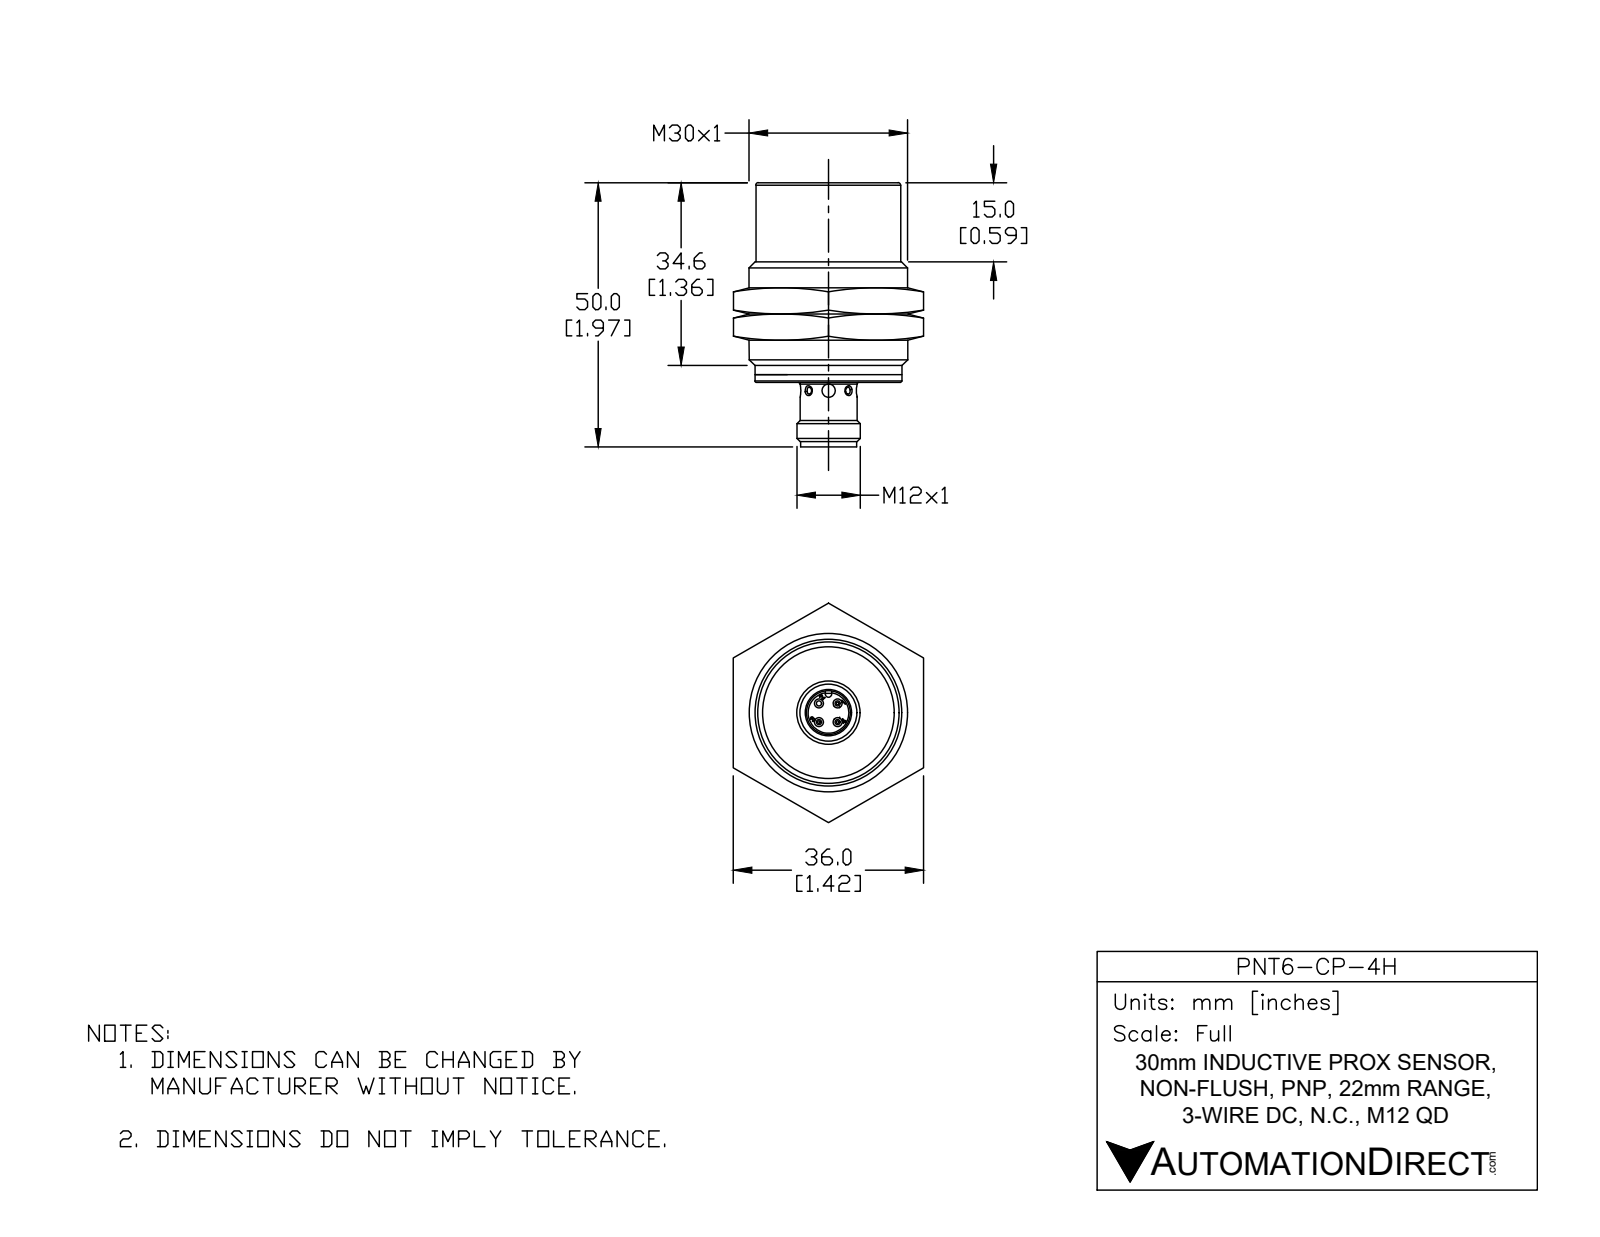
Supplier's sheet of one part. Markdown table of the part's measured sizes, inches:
| quantity | value |
| --- | --- |
| part name | PNT6-CP-4H |
| STEP written by | SolidWorks 2017 (AUTOMOTIVE_DESIGN) |
| units | inches |
| bodies | 1 solid, 515 faces (161 planar, 130 cylindrical, 224 other) |
| overall size | 1.969 × 1.181 × 1.181 |
| volume | 1.573 in³ |
| surface area | 12.79 in² |
| round holes (diameter × count) | 0.043 × 3, 0.04 × 2, 0.098 × 2, 0.038 × 1, 0.04 × 1, 0.323 × 1, 0.327 × 1, 0.394 × 1, 1.047 × 1, 1.076 × 1, 1.089 × 1 |
| round bosses / shafts (diameter × count) | 0.039 × 9, 1.181 × 1, 1.094 × 1, 1.083 × 1, 1.074 × 1, 1.044 × 1, 0.878 × 1, 0.472 × 1 |
| partial cylindrical surfaces (radius × count) | 0.004 × 12, 0.02 × 8, 0.03 × 3, 0.039 × 3, 0.024 × 1, 0.031 × 1 |
| main face-to-face distances | 0.126, 1.488, 1.362, 0.037, 0.089, 1.451, 0.098, 1.461, 0.028, 0.024 |
| hole center spacings | 0.098, 0.139, 0.197 |
